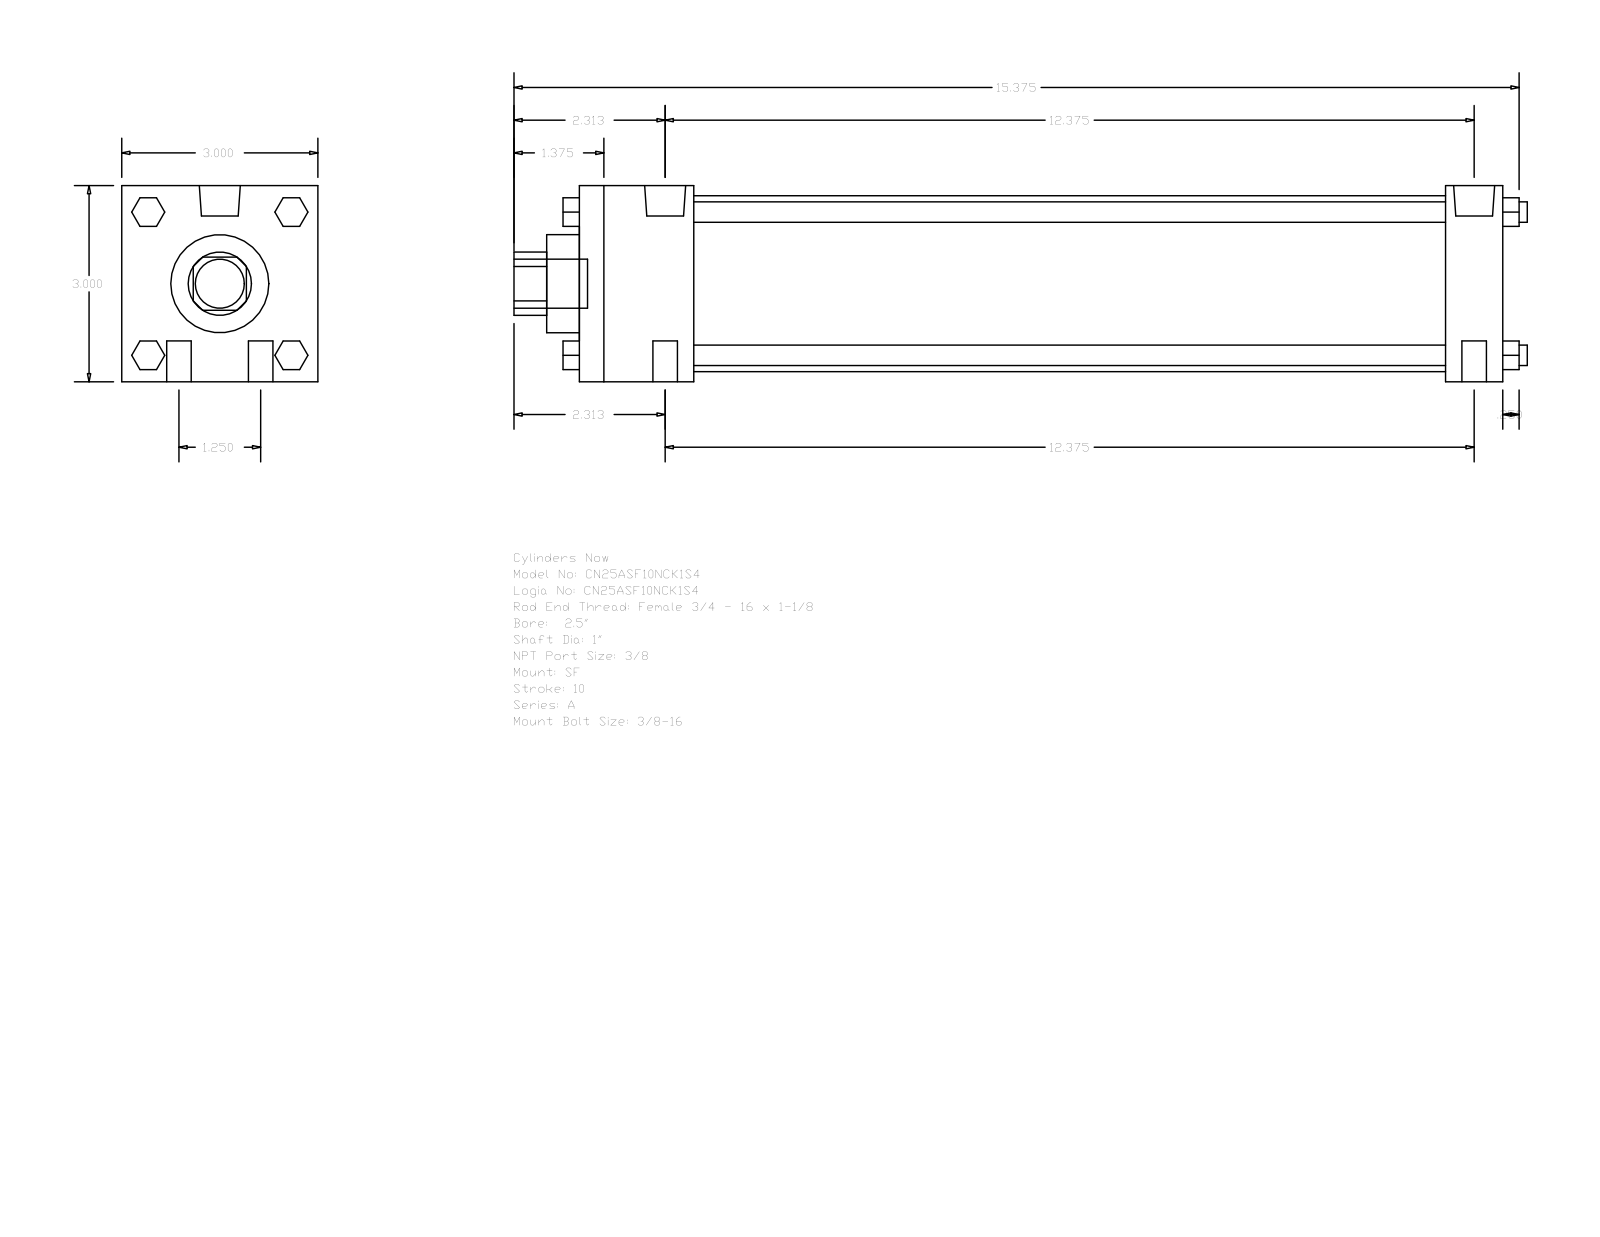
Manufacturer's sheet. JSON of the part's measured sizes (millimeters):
{"part_name": "A_SF__0250_1", "step_written_by": "GSSL Pune (CONFIG_CONTROL_DESIGN)", "units": "millimeters", "bodies": {"solids": 0, "faces": 124, "planar": 94, "cylindrical": 30, "other": 0}, "overall_size": [393.7, 76.2, 76.2], "round_holes": [[25.4, 1], [38.1, 1], [68.33, 1]], "round_bosses_or_shafts": [[9.53, 4], [7.94, 4], [15.93, 2], [5.56, 2], [19.05, 1]], "partial_cylinders_radius": [[12.29, 1]], "face_to_face_distances": [76.2, 358.78, 336.55, 22.23, 44.45, 292.1, 314.33, 12.7, 11.11, 57.15]}
